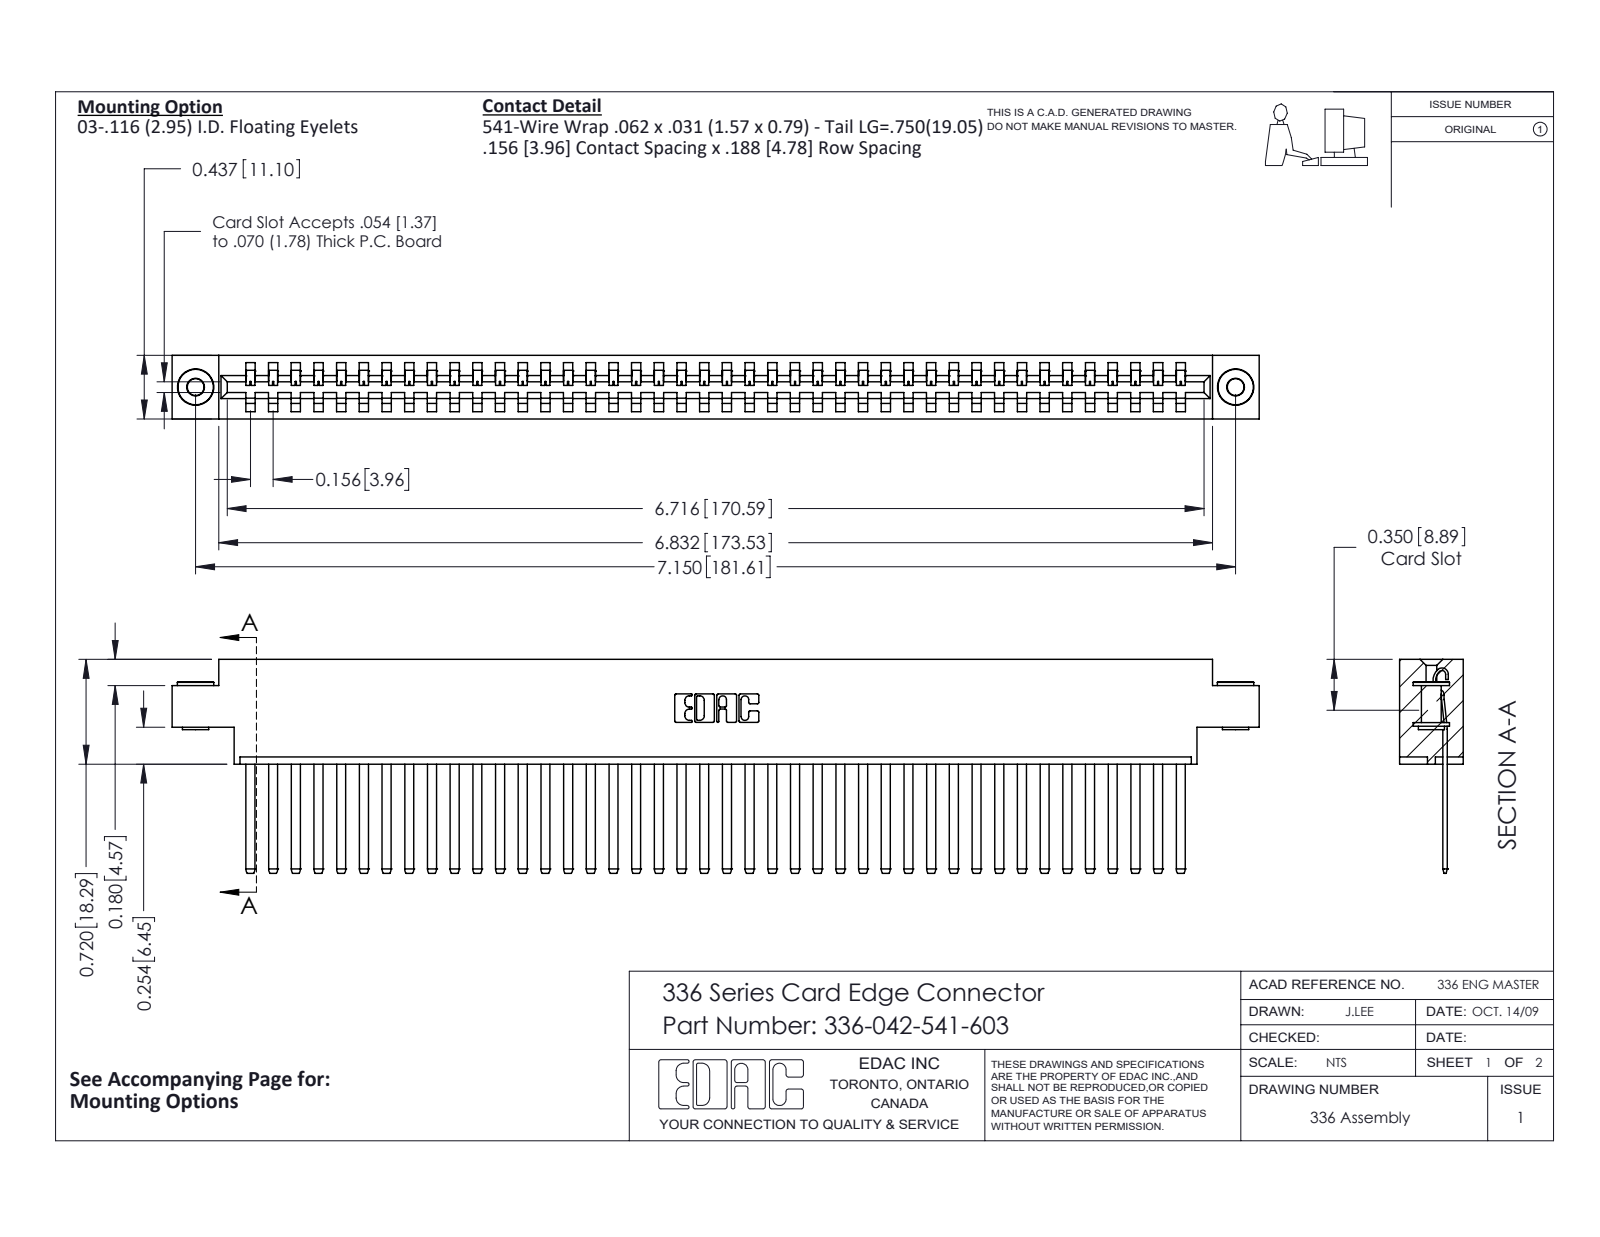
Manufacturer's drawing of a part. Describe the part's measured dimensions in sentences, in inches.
The part is named "336 Part_Offset - .156 Dia - TH; 336-290-001_336-290-541; 336-042-541-603; 345-250-002_345-250-002-102". Its 3-D file was written by "SolidWorks 2020 (CONFIG_CONTROL_DESIGN)". It is 45 solids with 2256 faces: 1512 planar, 736 cylindrical and 8 other. Overall it measures 7.473 by 1.47 by 0.437 inches. Its volume is 1.689 cubic inches and its surface area 47.17 square inches. Round holes: 2 of diameter 0.116, 2 of diameter 0.156. Round bosses or shafts: 2 of diameter 0.25, 2 of diameter 0.18, 2 of diameter 0.136. Partial cylindrical surfaces (rounded edges, fillets, slot ends): 84 of radius 0.004, 84 of radius 0.056, 22 of radius 0.01, 6 of radius 0.007, 6 of radius 0.031, 3 of radius 0.026, 2 of radius 0.022, 2 of radius 0.04. The main face-to-face distances are 0.437, 0.031, 0.181, 0.328, 0.14, 0.297, 0.109, 0.256, 0.05, 0.387. The hole center spacings are 7.15.
